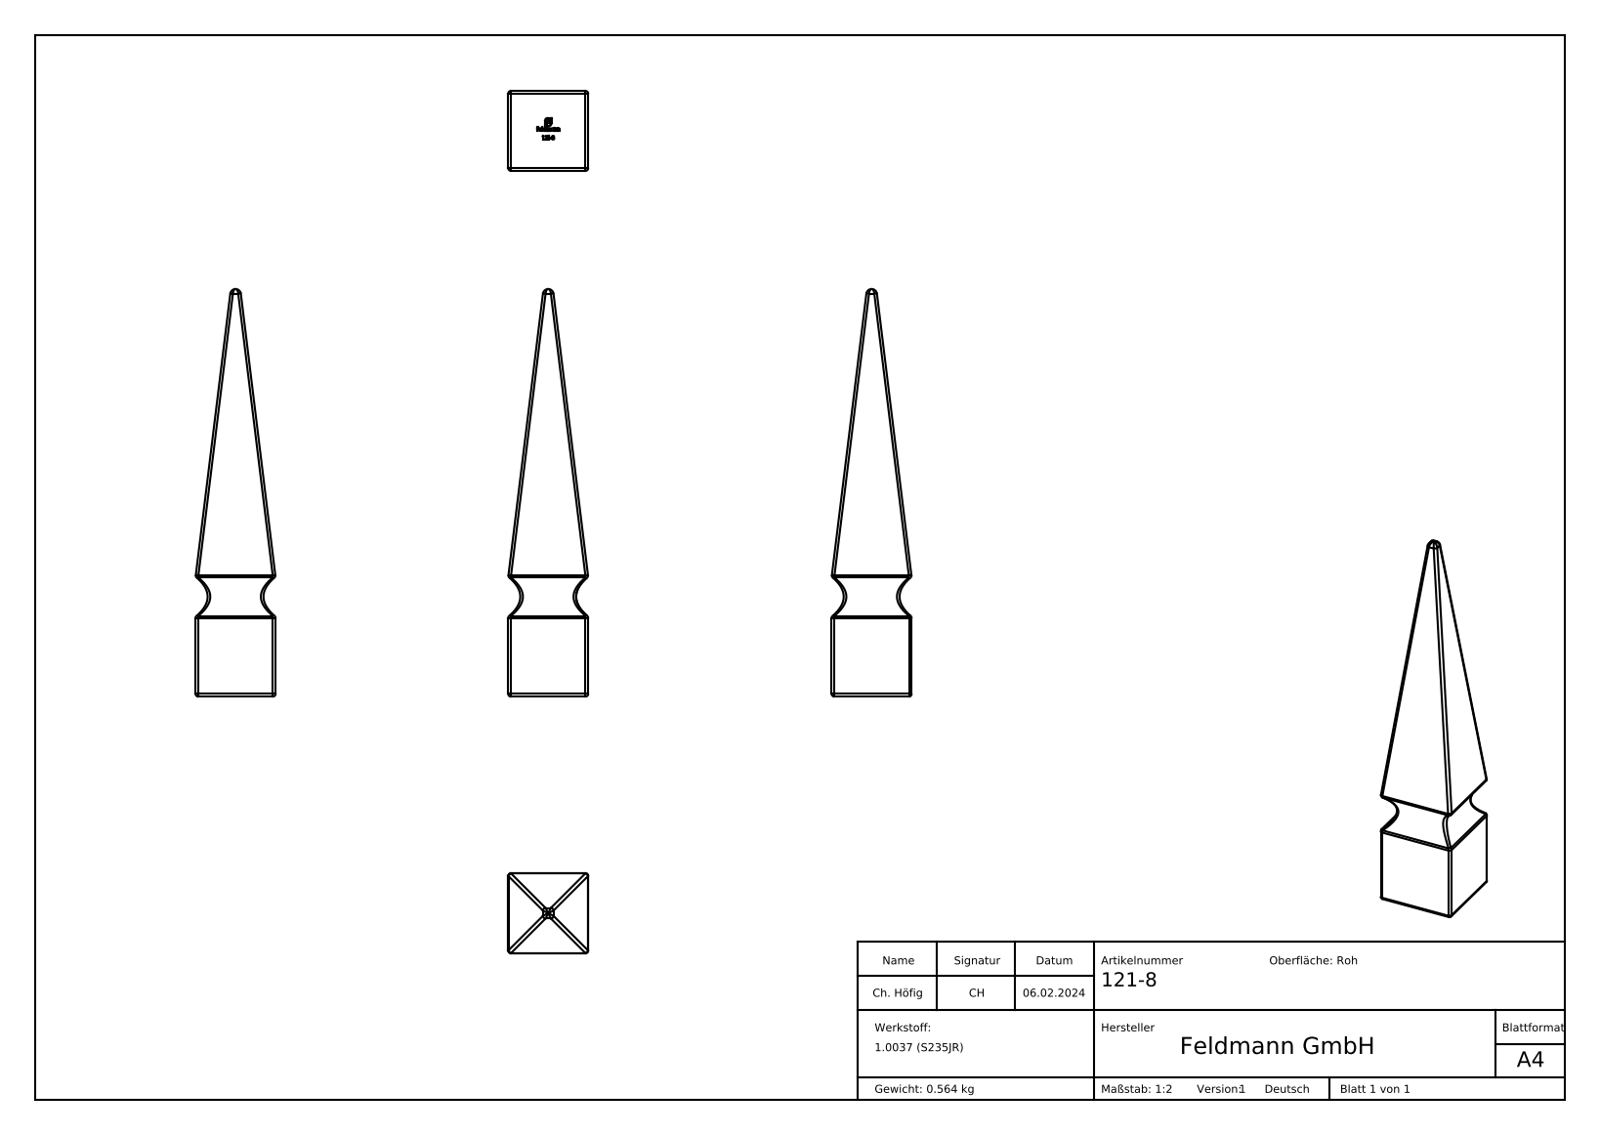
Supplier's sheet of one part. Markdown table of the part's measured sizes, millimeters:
| quantity | value |
| --- | --- |
| part name | 121-8 |
| STEP written by | SolidWorks 2018 (CONFIG_CONTROL_DESIGN) |
| units | millimeters |
| bodies | 1 solid, 265 faces (126 planar, 16 cylindrical, 123 other) |
| overall size | 153 × 30 × 30 |
| volume | 72 255 mm³ |
| surface area | 13 251 mm² |
| partial cylindrical surfaces (radius × count) | 1 × 12, 2 × 2 |
| main face-to-face distances | 30, 2.2, 2.52, 0.68, 3.27, 0.34, 15, 3.2, 13.99, 16.01 |
